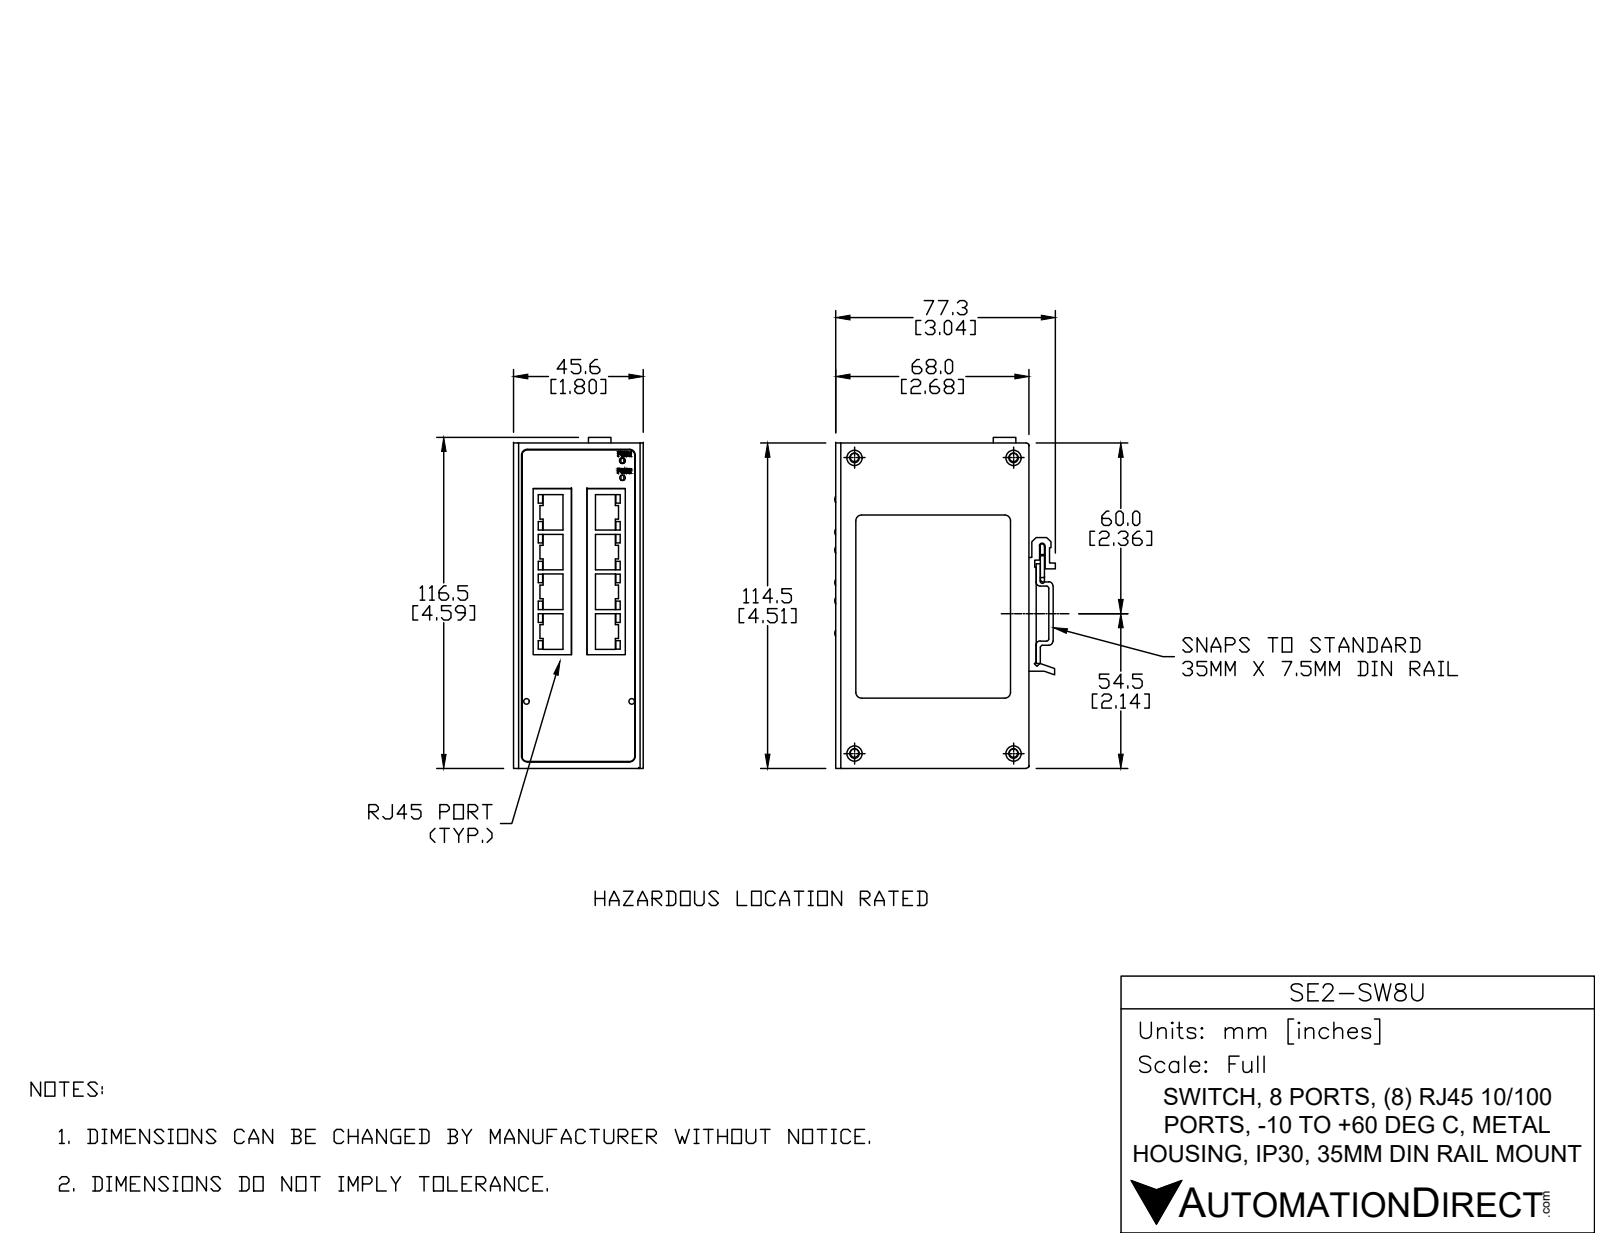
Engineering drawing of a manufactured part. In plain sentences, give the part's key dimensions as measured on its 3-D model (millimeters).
The part is named "SE2-SW8U". Its 3-D file was written by "SolidWorks 2019 (AUTOMOTIVE_DESIGN)". It is 17 solids with 1984 faces: 1394 planar, 499 cylindrical and 91 other. Overall it measures 125.8 by 77.2 by 45.6 millimeters. Its volume is 122 600 cubic millimeters and its surface area 122 800 square millimeters. Round holes: 6 of diameter 2.8, 6 of diameter 3, 4 of diameter 3.1, 4 of diameter 3.8, 3 of diameter 4, 2 of diameter 2.2, 2 of diameter 2.5, 2 of diameter 3.5, 1 of diameter 2. Round bosses or shafts: 8 of diameter 1.3, 4 of diameter 5, 4 of diameter 3.6, 4 of diameter 3, 4 of diameter 0.6, 1 of diameter 8, 1 of diameter 4. Partial cylindrical surfaces (rounded edges, fillets, slot ends): 120 of radius 0.6, 8 of radius 2, 8 of radius 3, 7 of radius 1, 4 of radius 0.3, 4 of radius 0.5, 4 of radius 1, 4 of radius 2.8. The main face-to-face distances are 1, 0.5, 43.6, 44.6, 2, 17.8, 43.1, 44.1, 1.5, 42.6. The hole center spacings are 22, 35.3, 56, 66.8, 104, 0.3, 3.2, 5.2.
